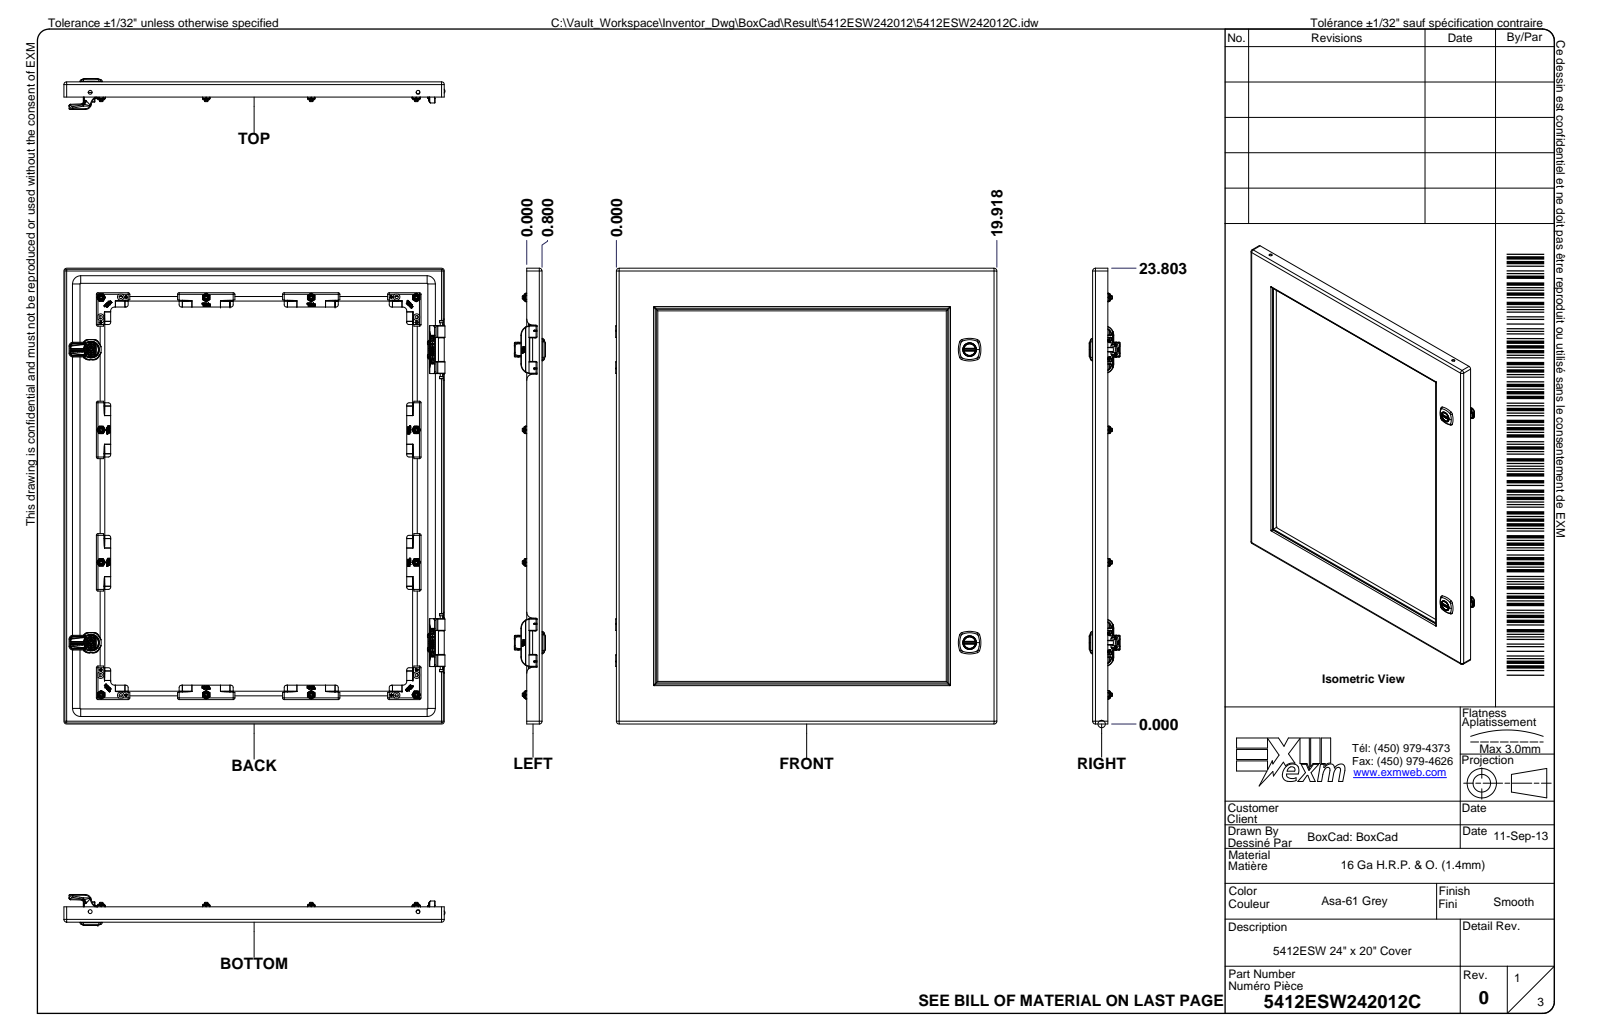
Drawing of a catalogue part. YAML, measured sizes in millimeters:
part_name: "5412ESW242012; 5412ESW242012B; 5412ESW242012B-P; STK-Q-16005 (+8 more)"
step_written_by: "Autodesk Inventor 2024 (AUTOMOTIVE_DESIGN)"
units: millimeters
bodies: {solids: 101, faces: 15779, planar: 6958, cylindrical: 3499, other: 5322}
overall_size: [609.6, 508.1, 338.1]
volume: 4275000
surface_area: 3866000
round_holes:
  - {diameter: 0.8, count: 17}
  - {diameter: 5.1, count: 16}
  - {diameter: 7.4, count: 16}
  - {diameter: 8, count: 16}
  - {diameter: 5, count: 12}
  - {diameter: 7, count: 12}
  - {diameter: 9.5, count: 12}
  - {diameter: 1.1, count: 8}
  - {diameter: 4.4, count: 8}
  - {diameter: 4.5, count: 4}
  - {diameter: 6.9, count: 4}
  - {diameter: 9.9, count: 4}
round_bosses_or_shafts:
  - {diameter: 5.9, count: 17}
  - {diameter: 0.8, count: 17}
  - {diameter: 9, count: 12}
  - {diameter: 6.9, count: 8}
  - {diameter: 1, count: 8}
  - {diameter: 18.2, count: 4}
  - {diameter: 7.9, count: 4}
  - {diameter: 6.7, count: 4}
partial_cylinders:
  - {radius: 0.5, count: 363}
  - {radius: 0.3, count: 139}
  - {radius: 1, count: 121}
  - {radius: 0.8, count: 110}
  - {radius: 0.2, count: 94}
  - {radius: 2.2, count: 68}
  - {radius: 0.4, count: 54}
  - {radius: 0.3, count: 50}
face_to_face_distances: [1.3, 506.7, 608.3, 23.5, 22.2, 26.2, 24.9, 2.7, 332.3, 317.7]
hole_center_spacings: [388.7, 139.7, 454.4, 545.2, 8.9, 18.7, 26.1, 26.7]
